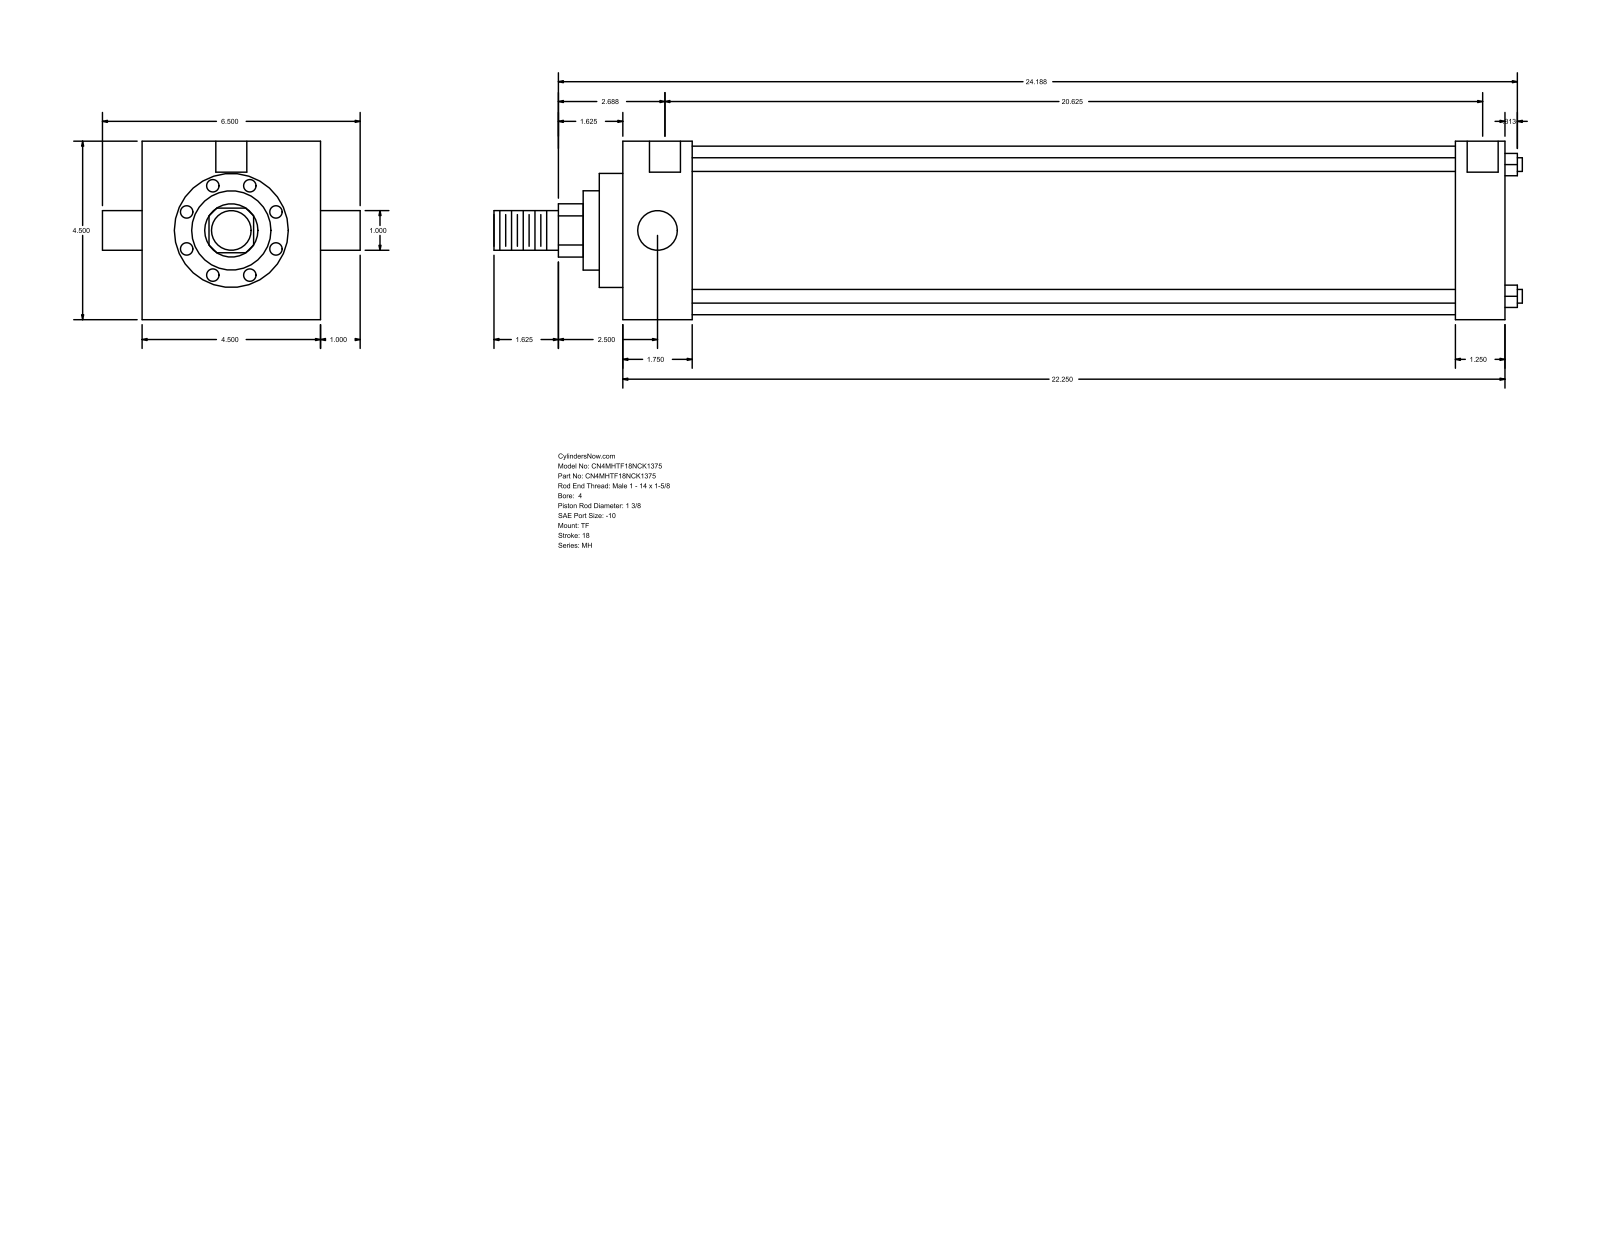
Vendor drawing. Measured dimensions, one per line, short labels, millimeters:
name: MH_TF__0400_1.375
written by: GSSL Pune (CONFIG_CONTROL_DESIGN)
unit: mm
bodies: 0 solids, 86 faces (61 planar, 25 cylindrical, 0 other)
size: 658.81 × 165.1 × 114.3
holes: 3× ⌀8.73, 2× ⌀19.84
bosses: 4× ⌀8.76, 2× ⌀25.4, 1× ⌀107.95, 1× ⌀73.03, 1× ⌀50.8, 1× ⌀34.92
rounds: 1× R17.06
face distances: 114.3, 565.15, 44.45, 520.7, 533.4, 488.95, 31.75, 15.08, 59.53, 548.48
hole spacings: 1.59, 525.47, 523.88, 527.06
